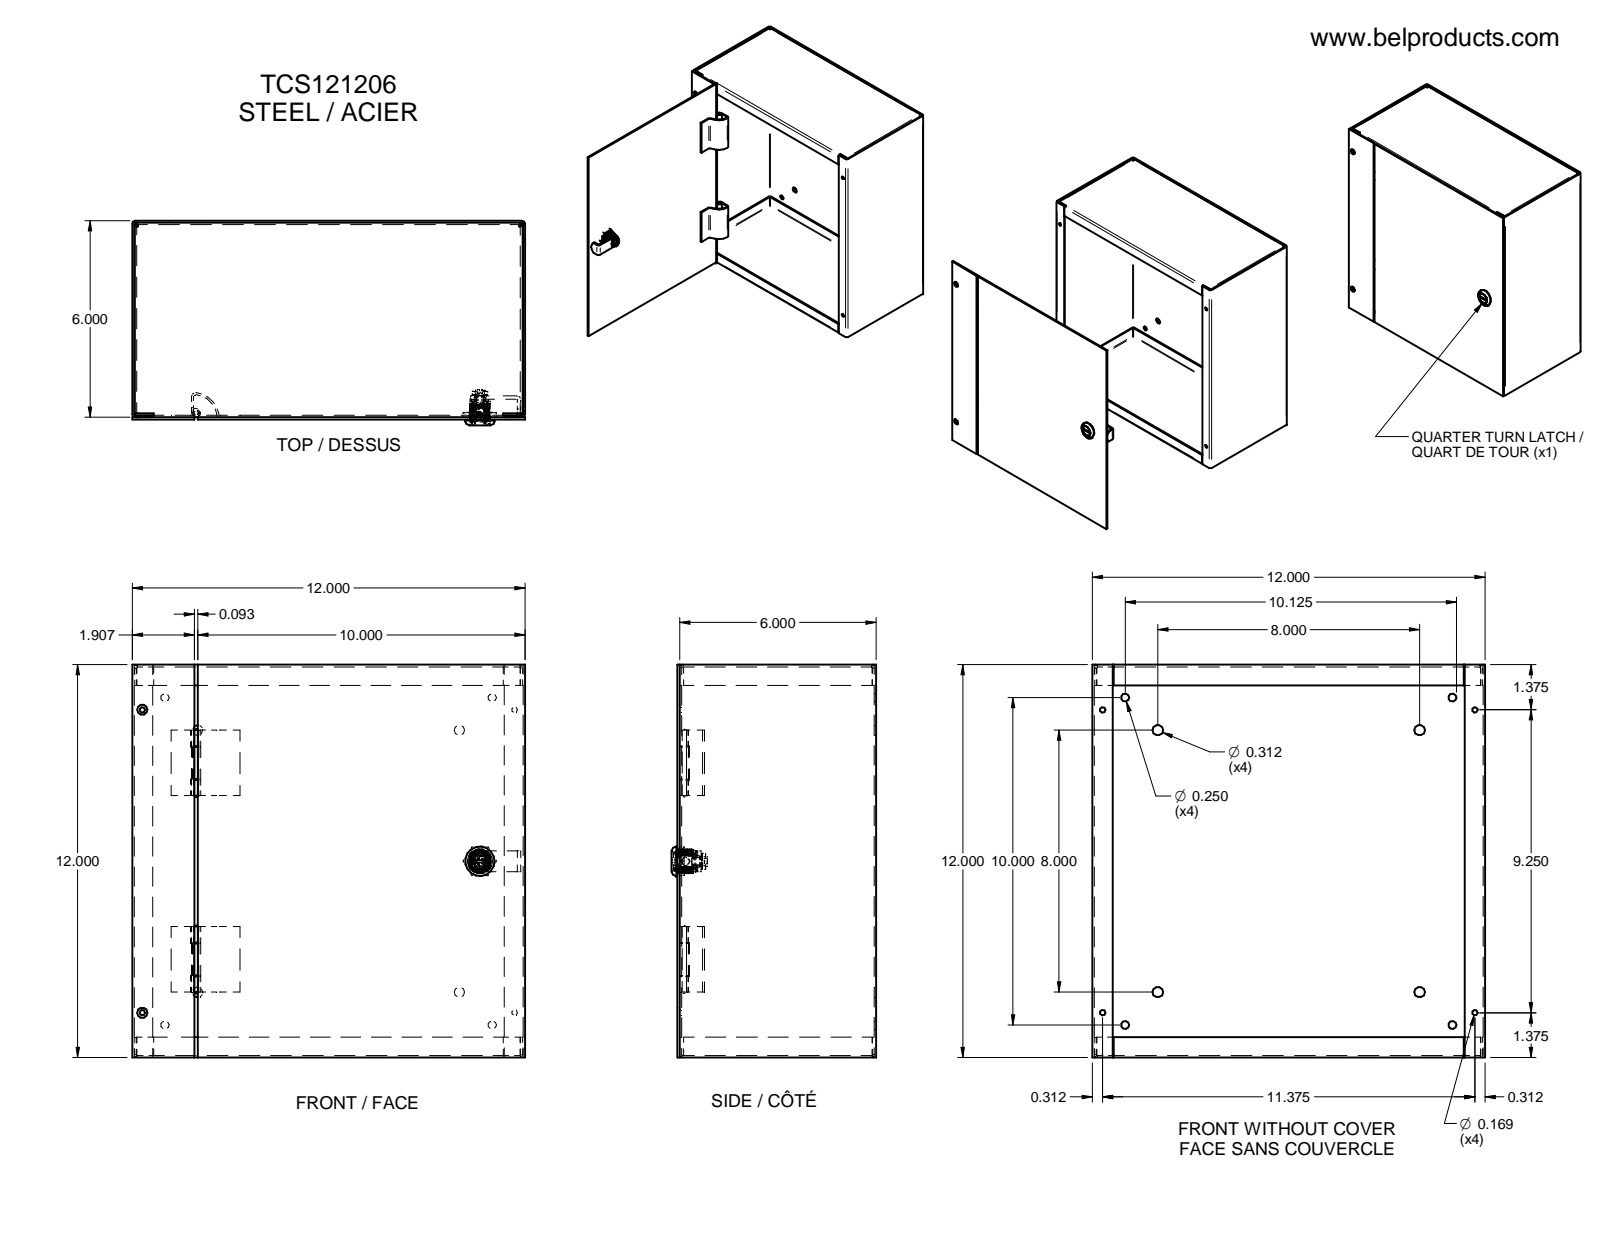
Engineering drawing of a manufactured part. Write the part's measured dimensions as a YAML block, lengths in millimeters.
part_name: "LOCK AVEC TOURNEVIS TYPE 4-12 SANS CAME; HOSING-oa0; INSERT POUR TOURNEVIS-oa1; NOIX DE FIXATION-oa2 (+8 more)"
step_written_by: "Unknown (AUTOMOTIVE_DESIGN)"
units: millimeters
bodies: {solids: 18, faces: 631, planar: 324, cylindrical: 161, other: 146}
overall_size: [304.8, 304.8, 158.78]
volume: 664925
surface_area: 835812
round_holes:
  - {diameter: 7.92, count: 6}
  - {diameter: 4.29, count: 4}
  - {diameter: 6.35, count: 4}
  - {diameter: 3.81, count: 1}
  - {diameter: 6.99, count: 1}
  - {diameter: 9.1, count: 1}
  - {diameter: 11.18, count: 1}
  - {diameter: 12.83, count: 1}
  - {diameter: 15.8, count: 1}
  - {diameter: 17.46, count: 1}
round_bosses_or_shafts:
  - {diameter: 22.86, count: 1}
  - {diameter: 22.61, count: 1}
  - {diameter: 15.75, count: 1}
  - {diameter: 12.95, count: 1}
  - {diameter: 12.62, count: 1}
  - {diameter: 12.19, count: 1}
  - {diameter: 11.86, count: 1}
  - {diameter: 10.08, count: 1}
partial_cylinders:
  - {radius: 0.81, count: 13}
  - {radius: 2.34, count: 12}
  - {radius: 9.53, count: 12}
  - {radius: 0.25, count: 8}
  - {radius: 1.52, count: 2}
  - {radius: 3.05, count: 2}
  - {radius: 9.42, count: 2}
  - {radius: 3.48, count: 1}
face_to_face_distances: [1.52, 303.28, 150.88, 1.91, 152.79, 152.4, 154.31, 304.8, 301.76, 3.43]
hole_center_spacings: [230.01, 19.89, 35.92, 45.7, 203.2, 223.22, 245.09, 246.57]
